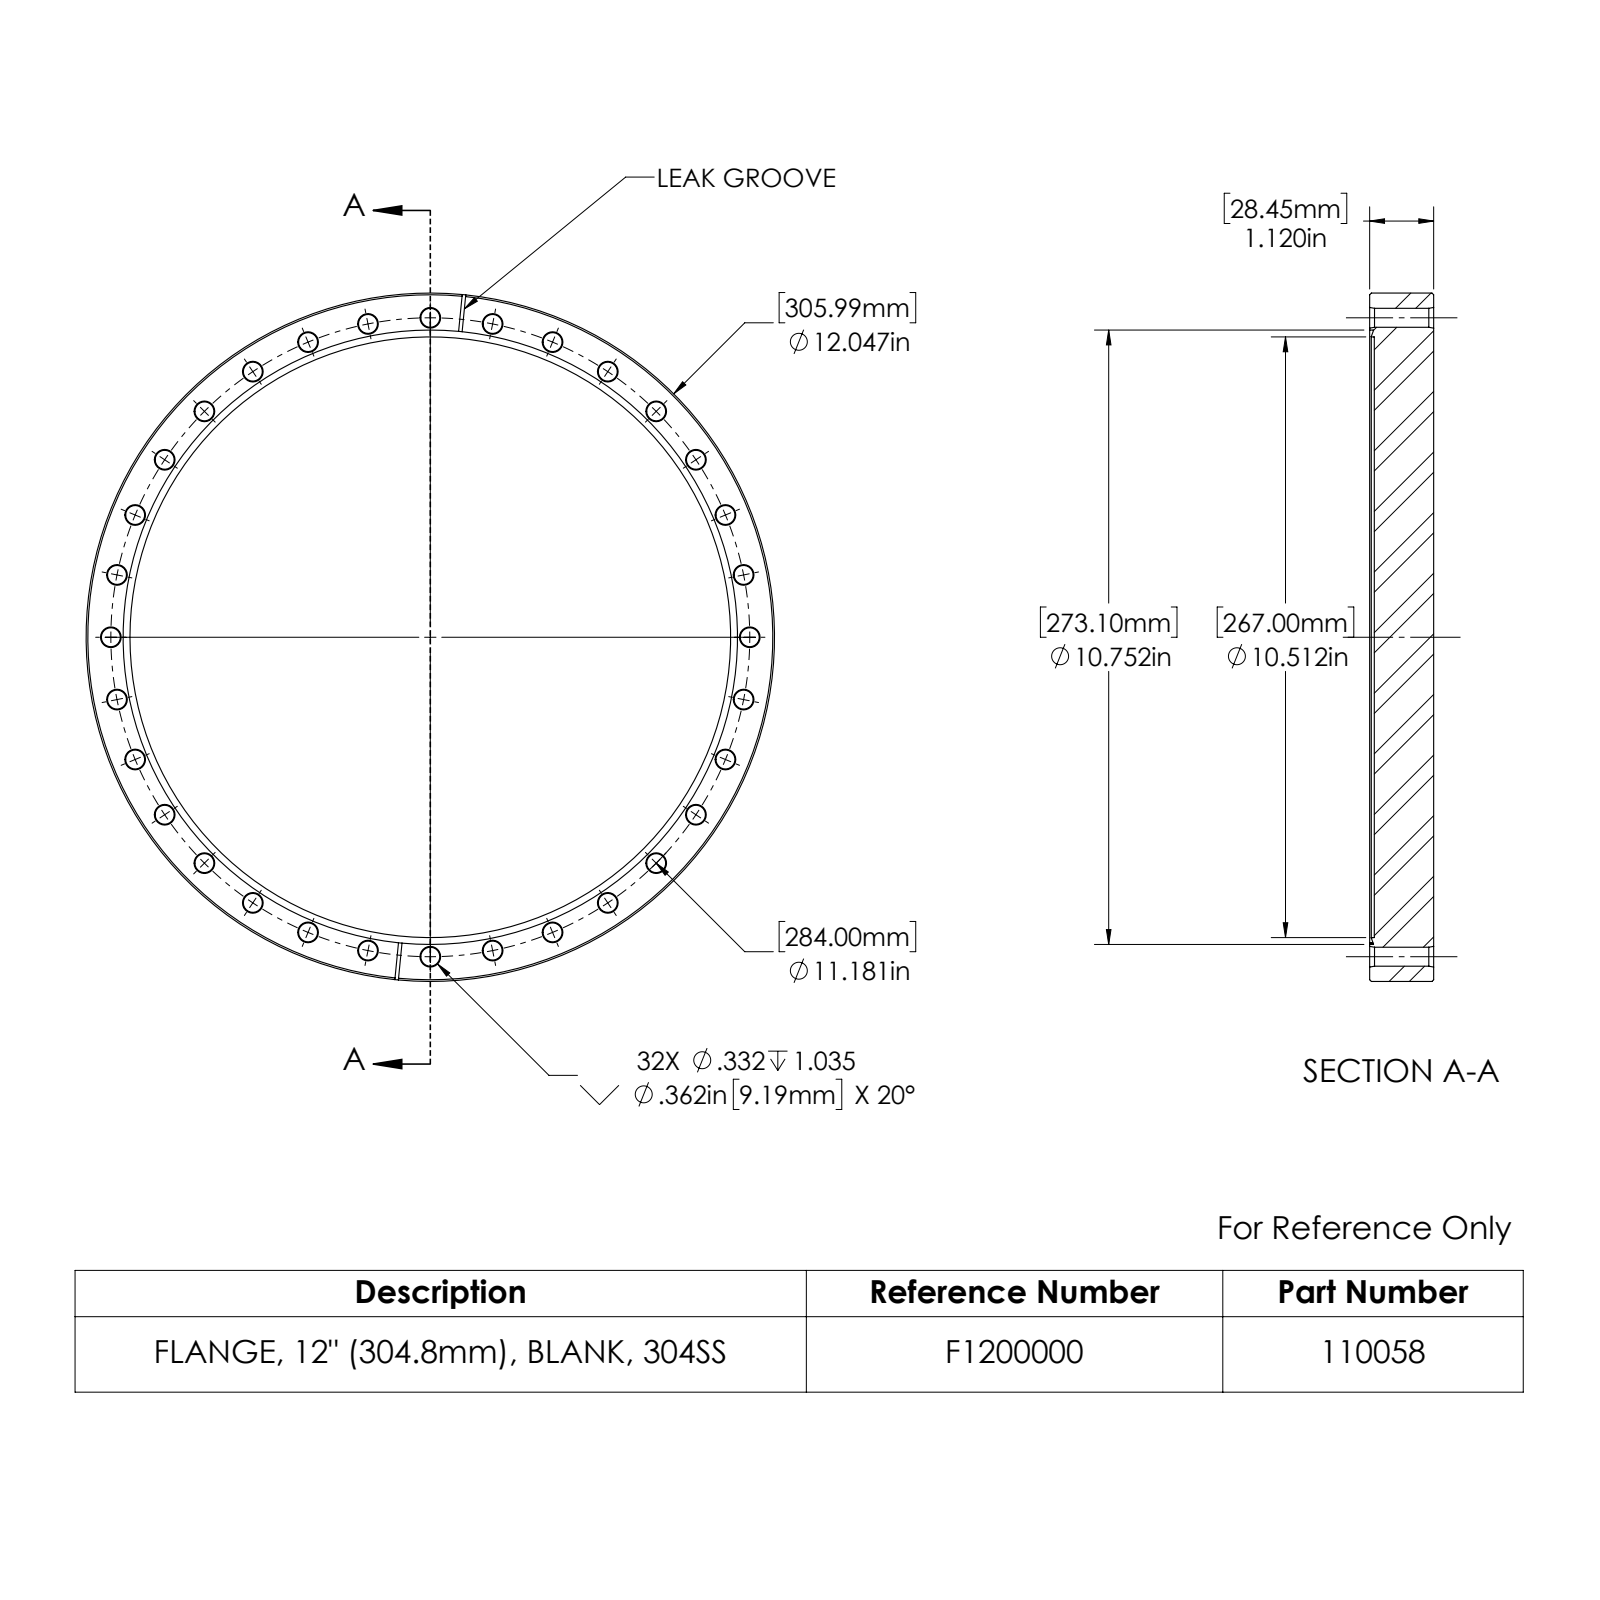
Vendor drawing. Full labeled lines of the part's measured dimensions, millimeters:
Part name (STEP PRODUCT): 110058
STEP written by: SolidWorks 2022 (AUTOMOTIVE_DESIGN)
Units: millimetres
Bodies: 1 solid, 221 faces (8 planar, 72 cylindrical, 141 other)
Overall size (bounding box): 306 × 306 × 28.4
Volume: 1 922 000 mm³ · Surface area: 196 500 mm²
Round holes (diameter × count): ⌀8.4 ×32, ⌀267 ×1, ⌀273.1 ×1
Round bosses / shafts (diameter × count): ⌀306 ×1
Partial cylindrical surfaces — rounded edges, fillets, slot ends (radius × count): R31.8 ×2
Main face-to-face distances: 26.4, 2.1, 28.4, 1.6, 1.6, 1.5
Hole centre spacings: 82.4, 157.8, 200.8, 262.4, 271.8, 278.5, 282.6, 236.1
